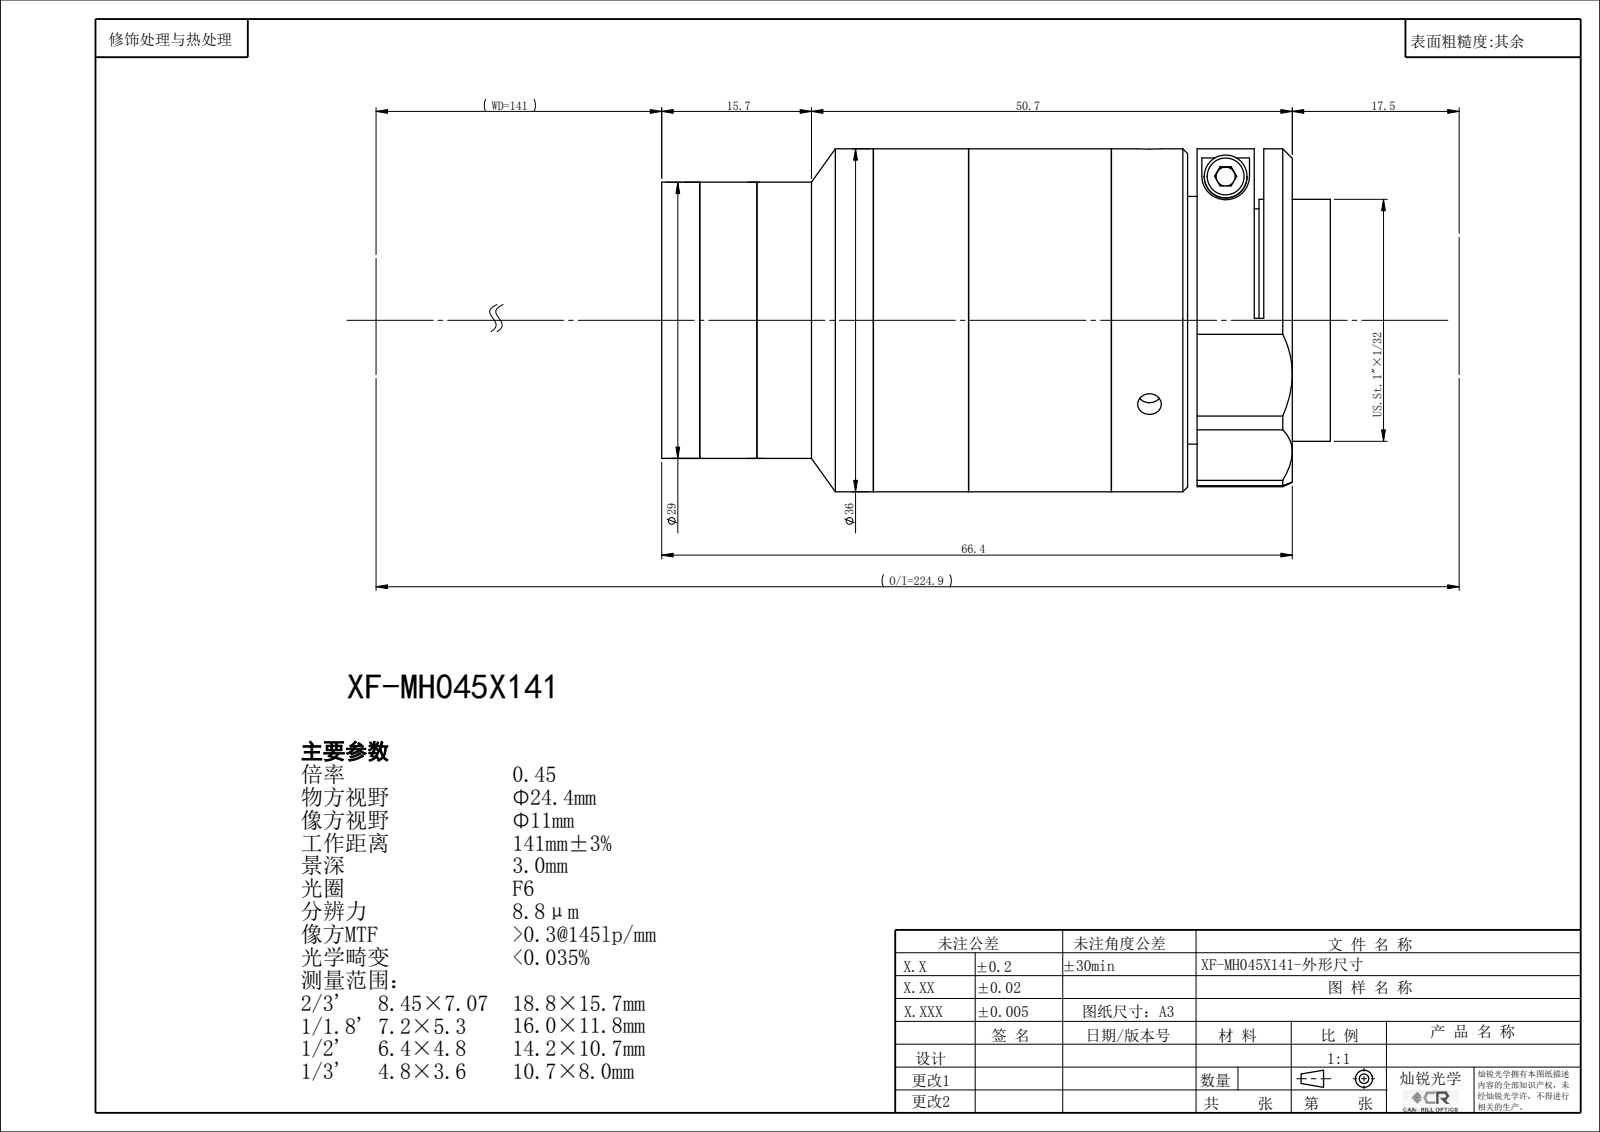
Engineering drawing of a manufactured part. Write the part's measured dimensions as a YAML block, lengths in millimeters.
part_name: "XF-MH045X141"
step_written_by: "SolidWorks 2022 (CONFIG_CONTROL_DESIGN)"
units: millimeters
bodies: {solids: 0, faces: 129, planar: 65, cylindrical: 42, other: 22}
overall_size: [70.39, 36.01, 36]
round_holes:
  - {diameter: 2.5, count: 3}
  - {diameter: 14, count: 1}
  - {diameter: 22.4, count: 1}
  - {diameter: 24, count: 1}
  - {diameter: 24.9, count: 1}
  - {diameter: 26, count: 1}
  - {diameter: 26.4, count: 1}
round_bosses_or_shafts:
  - {diameter: 36, count: 1}
  - {diameter: 34, count: 1}
  - {diameter: 29, count: 1}
  - {diameter: 25.4, count: 1}
face_to_face_distances: [19.15, 43.44, 62.59, 1.5, 61.09, 17.65, 10, 28.44, 15, 32.65]
